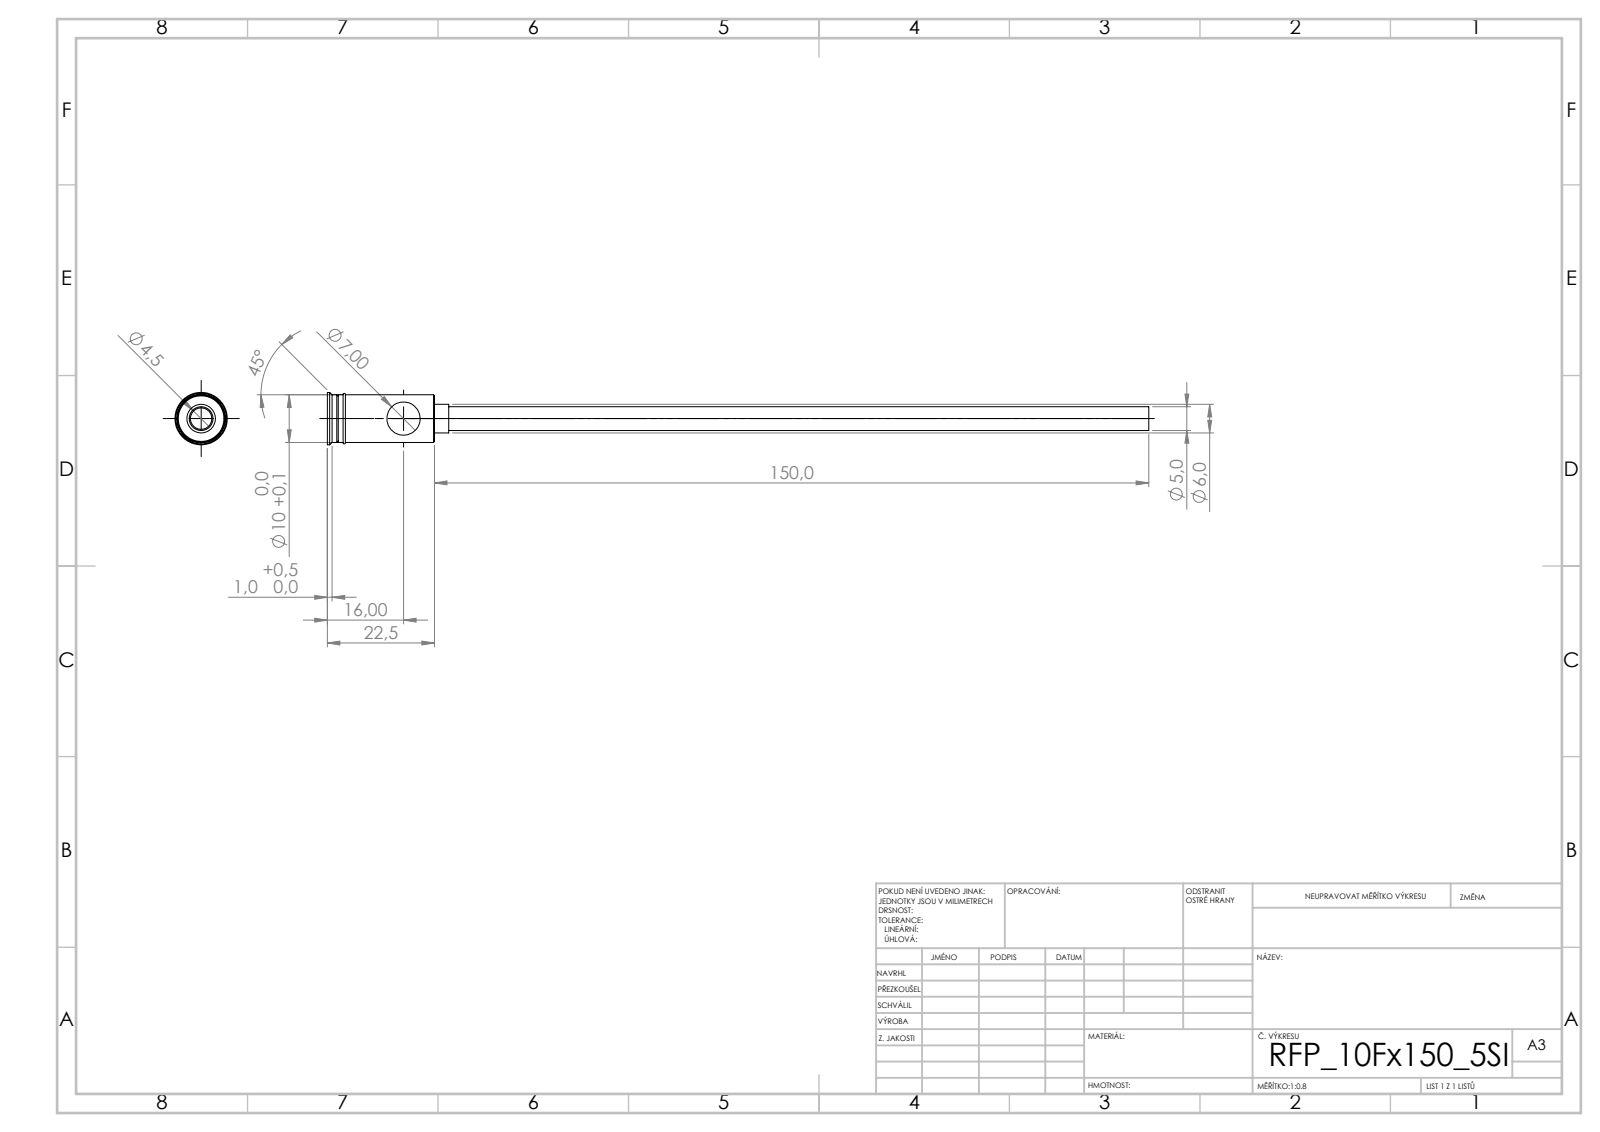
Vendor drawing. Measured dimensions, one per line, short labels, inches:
written by: SolidWorks 2019 (CONFIG_CONTROL_DESIGN)
unit: in
bodies: 1 solid, 44 faces (20 planar, 16 cylindrical, 8 other)
size: 6.791 × 0.433 × 0.433
volume: 0.116 in³; area: 8.61 in²
holes: 1× ⌀0.177, 1× ⌀0.276
bosses: 1× ⌀0.433, 1× ⌀0.394, 1× ⌀0.236, 1× ⌀0.197
face distances: 0.886, 0.807, 0.079, 0.213, 0.795, 0.091, 0.118, 0.913, 0.925, 1.004
